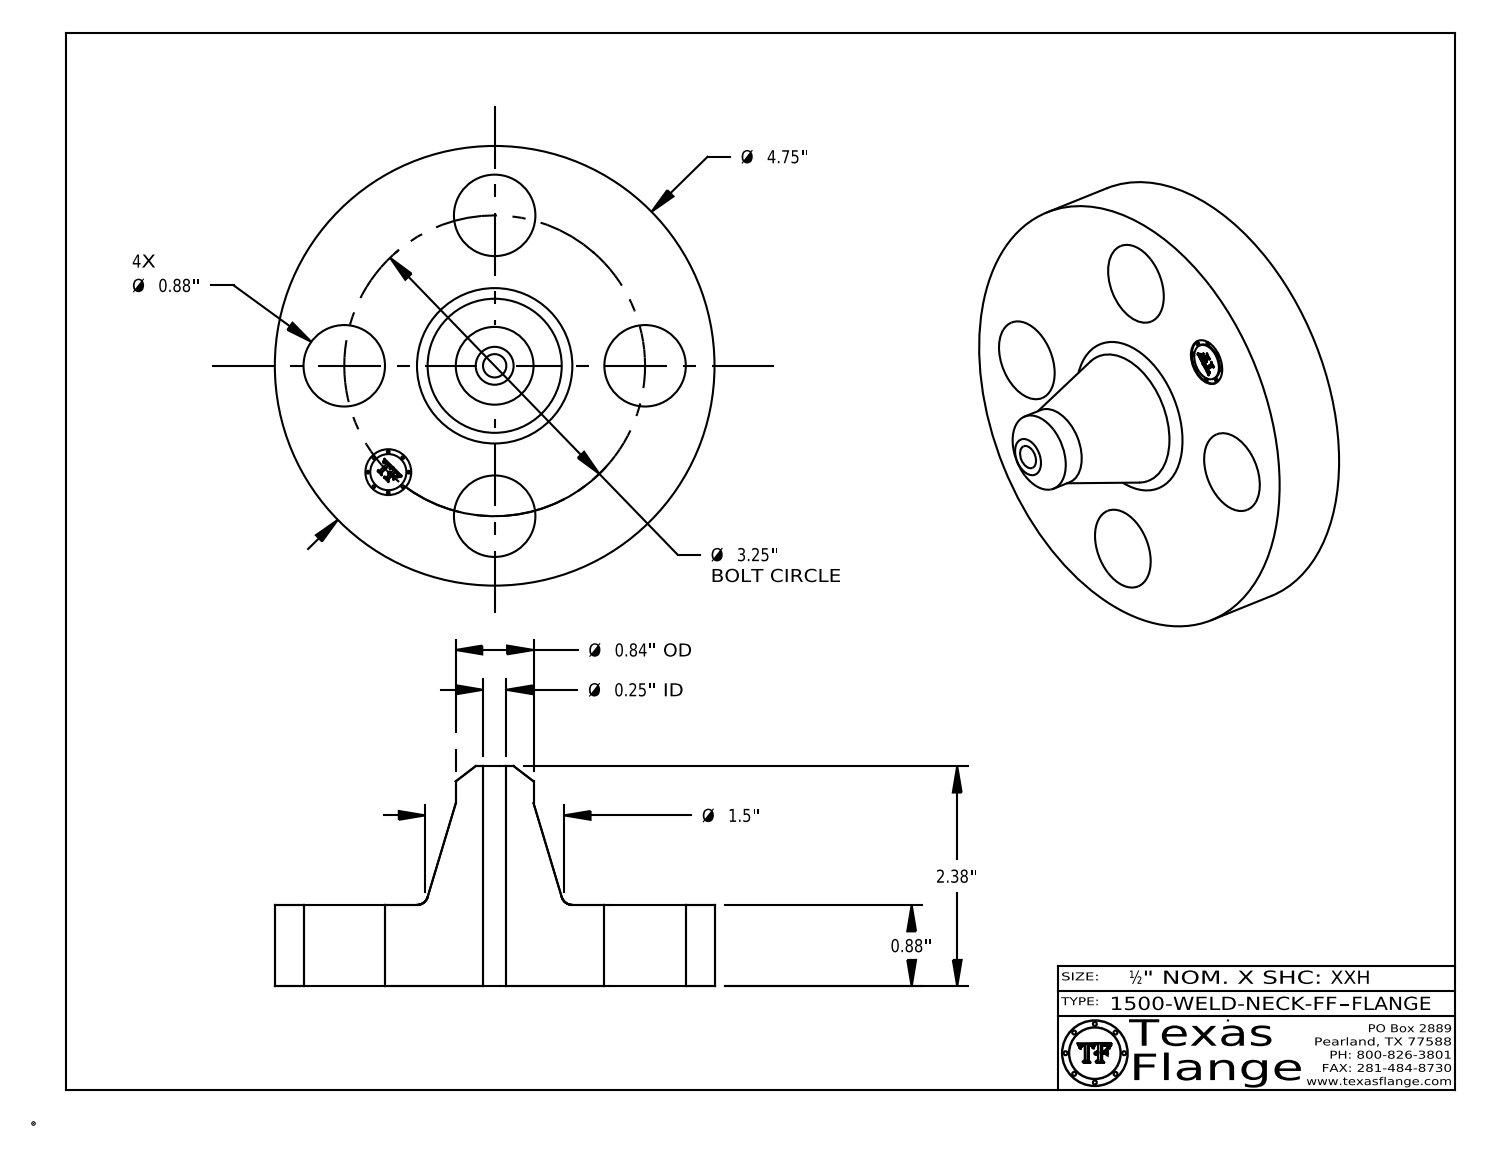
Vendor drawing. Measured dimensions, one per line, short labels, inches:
name: 1500-WELD-NECK-FF
written by: CATIA V5 STEP AP214 (AUTOMOTIVE_DESIGN)
unit: in
bodies: 1 solid, 408 faces (368 planar, 34 cylindrical, 6 other)
size: 4.75 × 4.75 × 2.38
volume: 14.74 in³; area: 58.94 in²
holes: 4× ⌀0.88, 1× ⌀0.252, 1× ⌀0.495
bosses: 8× ⌀0.03, 1× ⌀4.75, 1× ⌀0.84, 1× ⌀0.39
face distances: 0.88, 2.38, 1.5, 0.865, 0.015, 1.515, 0.148, 0.144, 0.027, 0.096
hole spacings: 1.625, 2.298, 1.244, 3.003, 3.25
